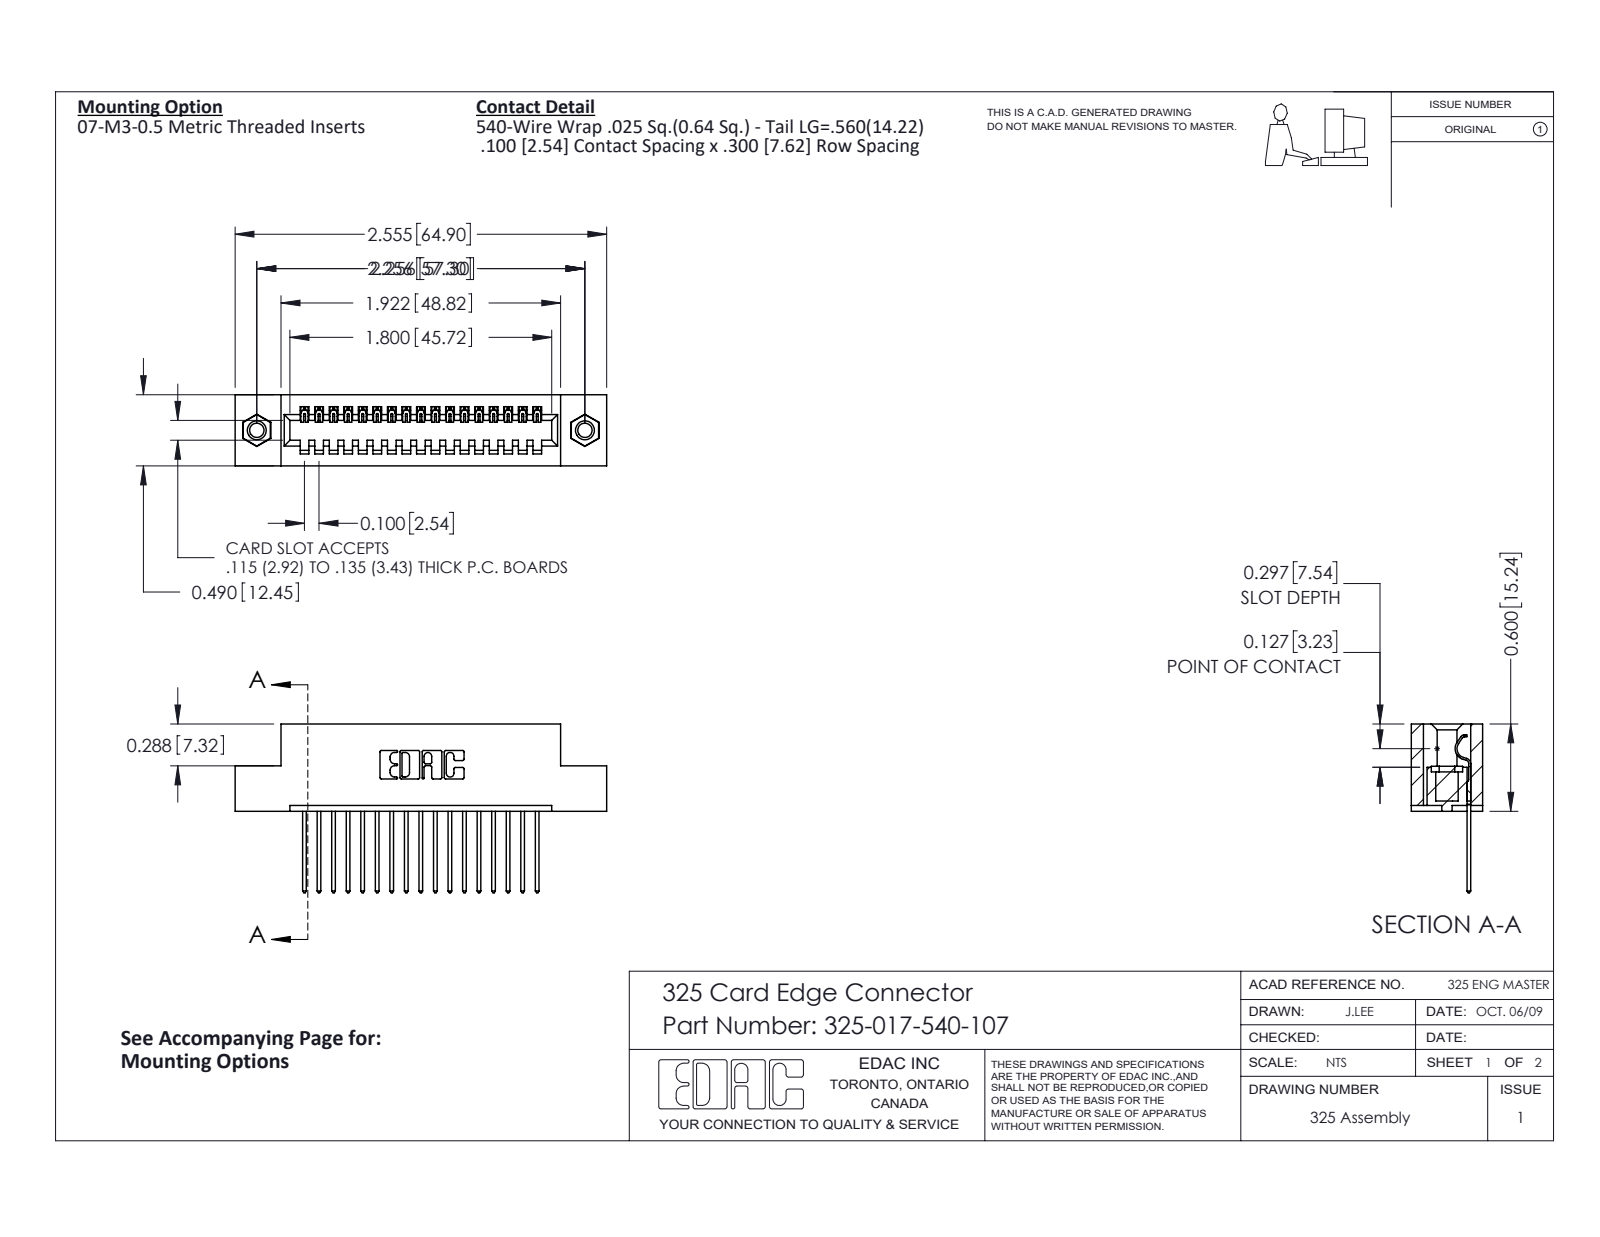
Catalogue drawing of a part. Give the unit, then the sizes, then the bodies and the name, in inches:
Units: inches
Overall size (bounding box): 2.555 × 1.16 × 0.49
Round holes (diameter × count): ⌀0.098 ×2, ⌀0.125 ×2, ⌀0.16 ×2
Round bosses / shafts (diameter × count): ⌀0.155 ×2
Partial cylindrical surfaces — rounded edges, fillets, slot ends (radius × count): R0.006 ×34, R0.01 ×34, R0.01 ×22, R0.007 ×6, R0.031 ×6, R0.026 ×3, R0.014 ×1, R0.022 ×1
Main face-to-face distances: 0.083, 0.407, 0.3, 0.49, 0.107, 0.383, 0.025, 0.6, 0.04, 0.2
Hole centre spacings: 2.256
Volume: 0.491 in³ · Surface area: 13.28 in²
Bodies: 20 solids, 1160 faces (816 planar, 328 cylindrical, 16 other)
Part name (STEP PRODUCT): 325-017-540-107; 325 Part_TI; 325-292-001_325-293-140; 345-250-001_345-250-005-103
STEP written by: SolidWorks 2016 (CONFIG_CONTROL_DESIGN)
